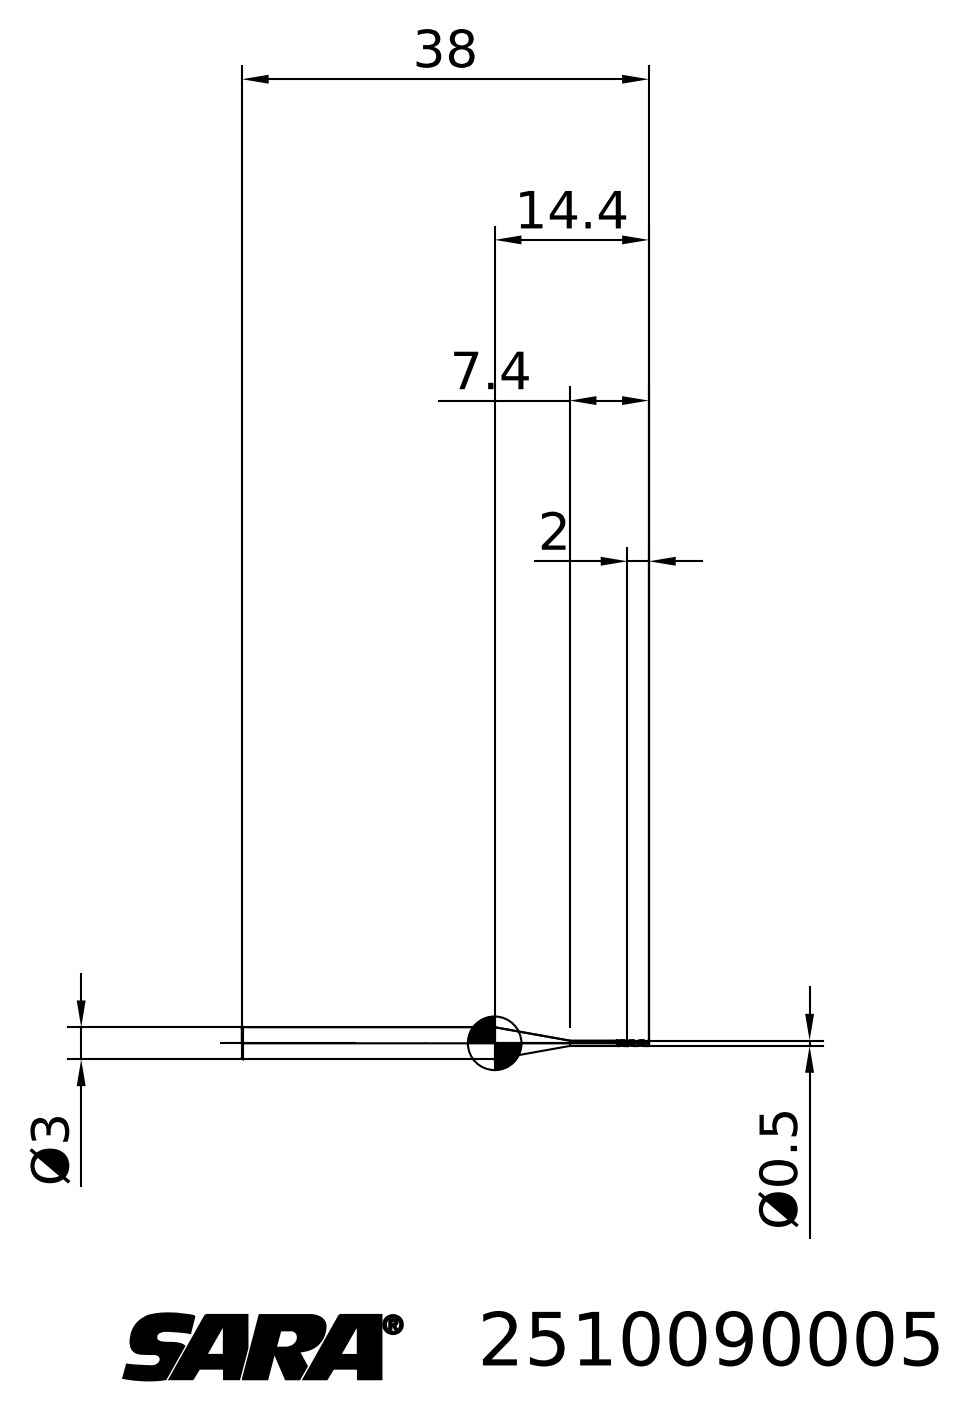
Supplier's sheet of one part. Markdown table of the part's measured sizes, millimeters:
| quantity | value |
| --- | --- |
| STEP written by | TDM (AUTOMOTIVE_DESIGN) |
| units | millimeters |
| bodies | 2 solids, 26 faces (4 planar, 0 cylindrical, 22 other) |
| overall size | 38 × 3 × 3 |
| volume | 188 mm³ |
| surface area | 280 mm² |
| main face-to-face distances | 36, 2, 38 |
